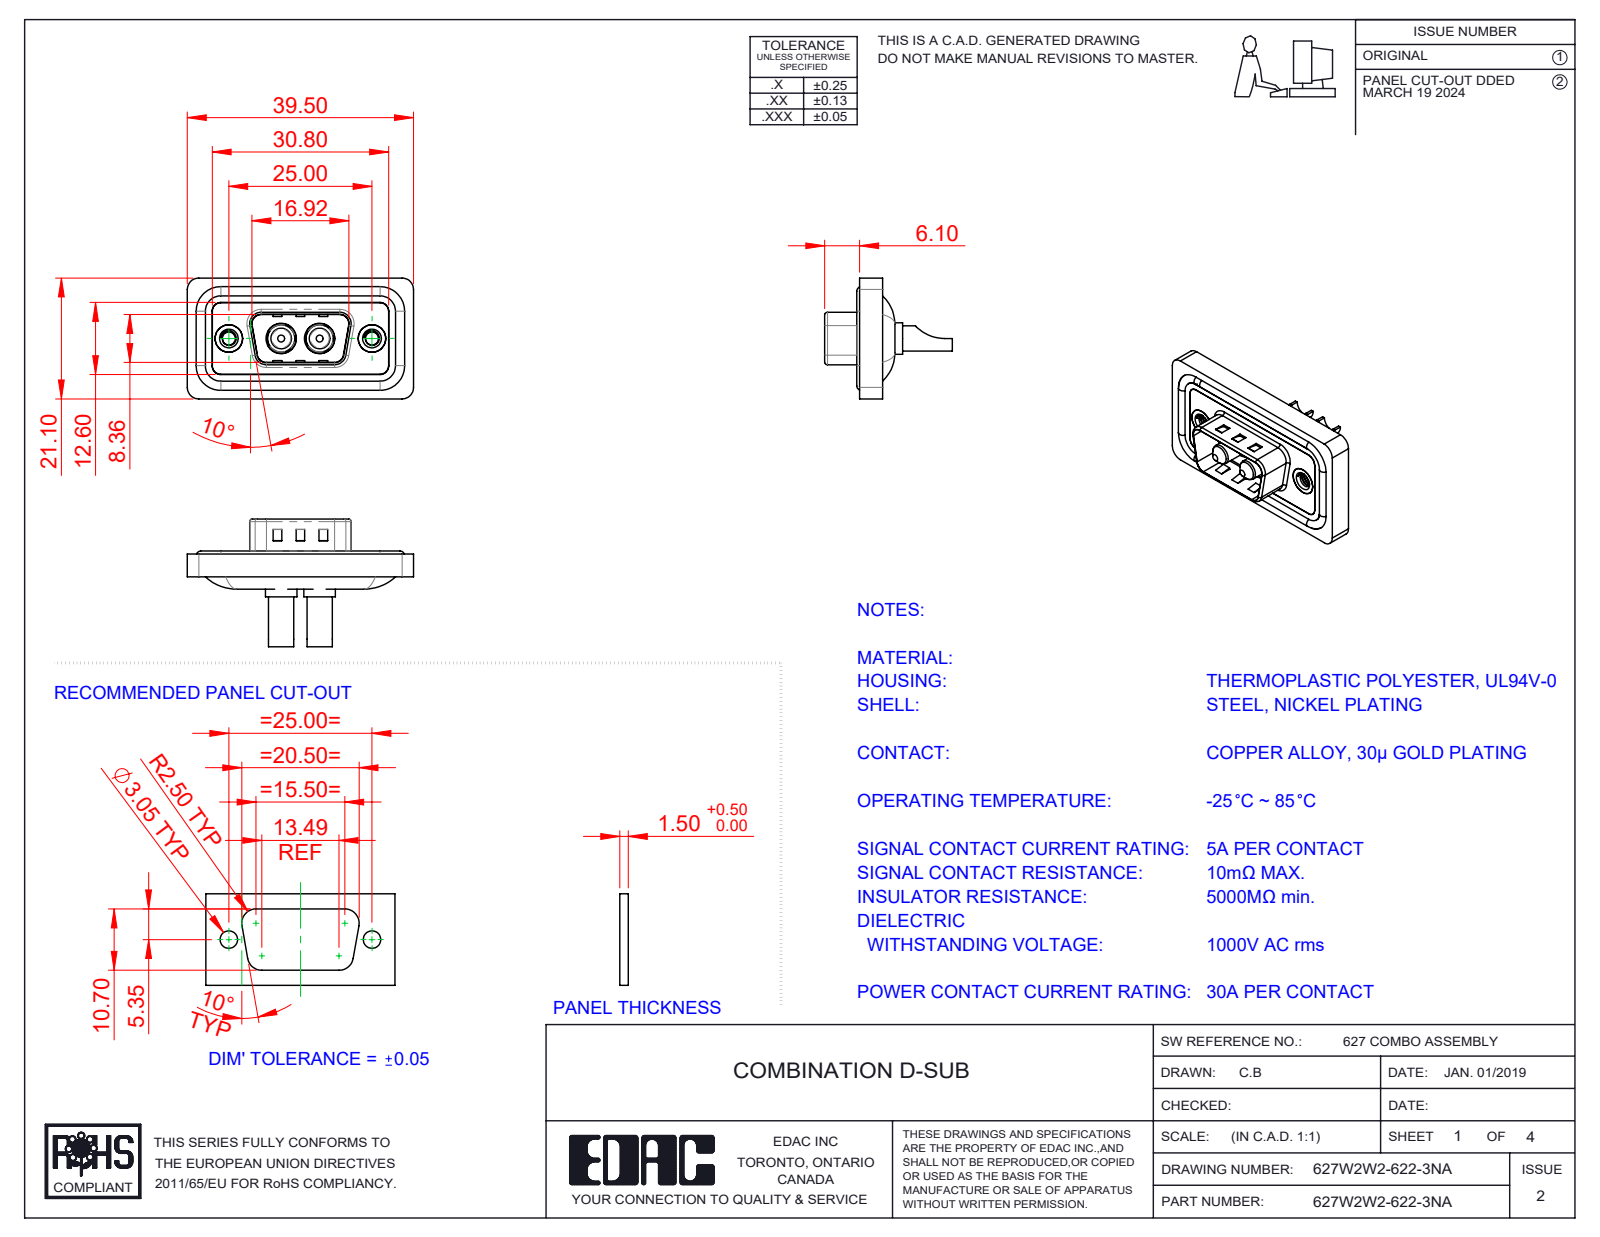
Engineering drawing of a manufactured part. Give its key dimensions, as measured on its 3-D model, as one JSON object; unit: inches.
{"part_name": "627Combo Housing_2W2; 627W2W2-622-3NA; 627Combo Shell Rear_09 Contacts; 627Combo Threaded Rivet_A (+3 more)", "step_written_by": "SolidWorks 2023 (CONFIG_CONTROL_DESIGN)", "units": "inches", "bodies": {"solids": 11, "faces": 499, "planar": 171, "cylindrical": 226, "other": 102}, "overall_size": [1.555, 0.878, 0.831], "volume_in3": 0.275, "surface_area_in2": 11.16, "round_holes": [[0.089, 2], [0.138, 2], [0.157, 2], [0.189, 2], [0.191, 2], [0.197, 2], [0.209, 2]], "round_bosses_or_shafts": [[0.063, 4], [0.217, 2], [0.205, 2], [0.193, 2], [0.187, 2], [0.173, 2], [0.148, 2], [0.142, 2]], "partial_cylinders_radius": [[0.059, 22], [0.079, 18], [0.02, 8], [0.063, 8], [0.01, 4], [0.024, 4], [0.026, 4], [0.035, 4]], "face_to_face_distances": [0.016, 0.043, 0.114, 0.122, 0.02, 0.063, 0.059, 0.098, 0.157, 0.028], "hole_center_spacings": [0.36, 0.624, 0.265, 0.984]}
